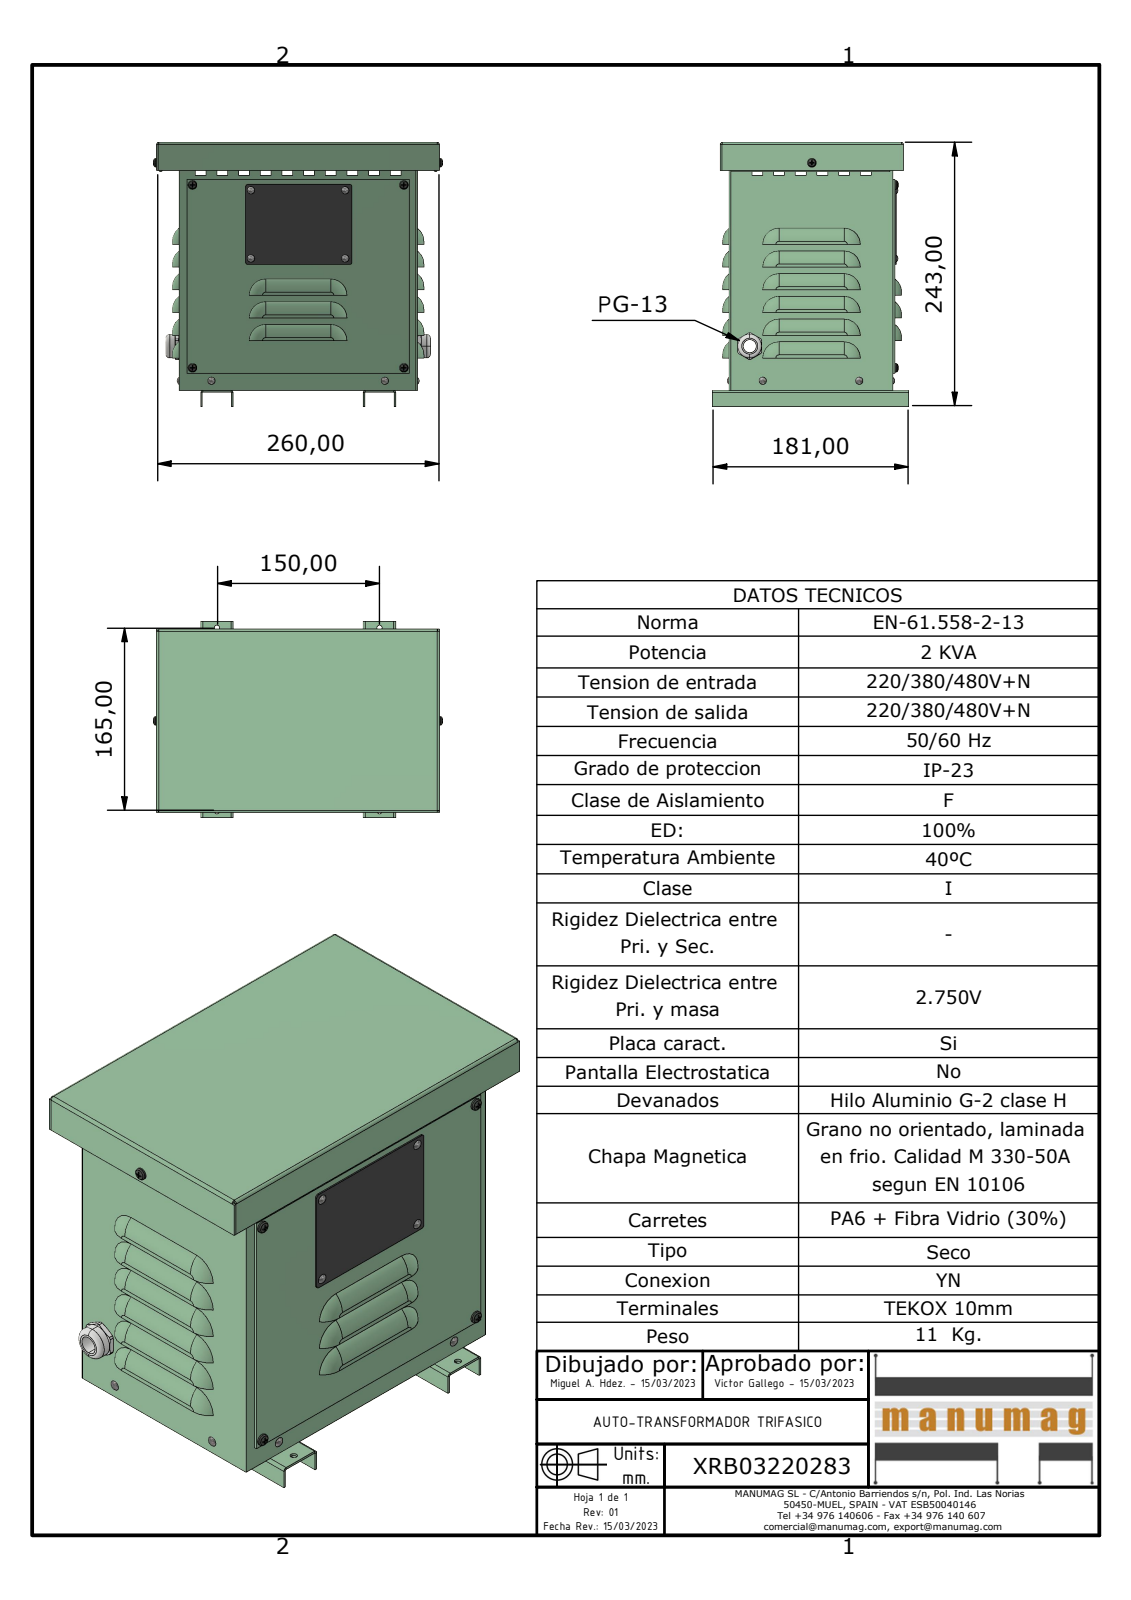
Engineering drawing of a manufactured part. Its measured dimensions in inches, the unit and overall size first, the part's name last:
Units: inches
Overall size (bounding box): 10.517 × 9.626 × 7.126
Round holes (diameter × count): ⌀0.189 ×13, ⌀0.15 ×5, ⌀0.118 ×4, ⌀0.157 ×4, ⌀0.472 ×1, ⌀0.866 ×1
Round bosses / shafts (diameter × count): ⌀0.126 ×8, ⌀0.157 ×5, ⌀0.143 ×5, ⌀0.854 ×1, ⌀0.803 ×1, ⌀0.799 ×1, ⌀0.746 ×1
Partial cylindrical surfaces — rounded edges, fillets, slot ends (radius × count): R0.551 ×24, R0.591 ×21, R0.157 ×18, R0.059 ×13, R0.079 ×12, R0.02 ×8, R0.098 ×8, R0.571 ×6
Main face-to-face distances: 0.059, 5.886, 8.976, 8.602, 9.035, 5.965, 5.945, 0.079, 6.024, 8.543
Hole centre spacings: 6.654, 5.906, 0.835, 1.024, 1.693, 1.969, 2.135, 2.48
Volume: 36.69 in³ · Surface area: 1 038 in²
Bodies: 27 solids, 1168 faces (639 planar, 259 cylindrical, 270 other)
Part name (STEP PRODUCT): XRB03220283; JE001 - JE002 EXPORT CUERPO; JE001 - JE002 EXPORT BASE; JE001 - JE002 EXPORT PATA (+6 more)
STEP written by: Autodesk Inventor 2023 (AUTOMOTIVE_DESIGN)
